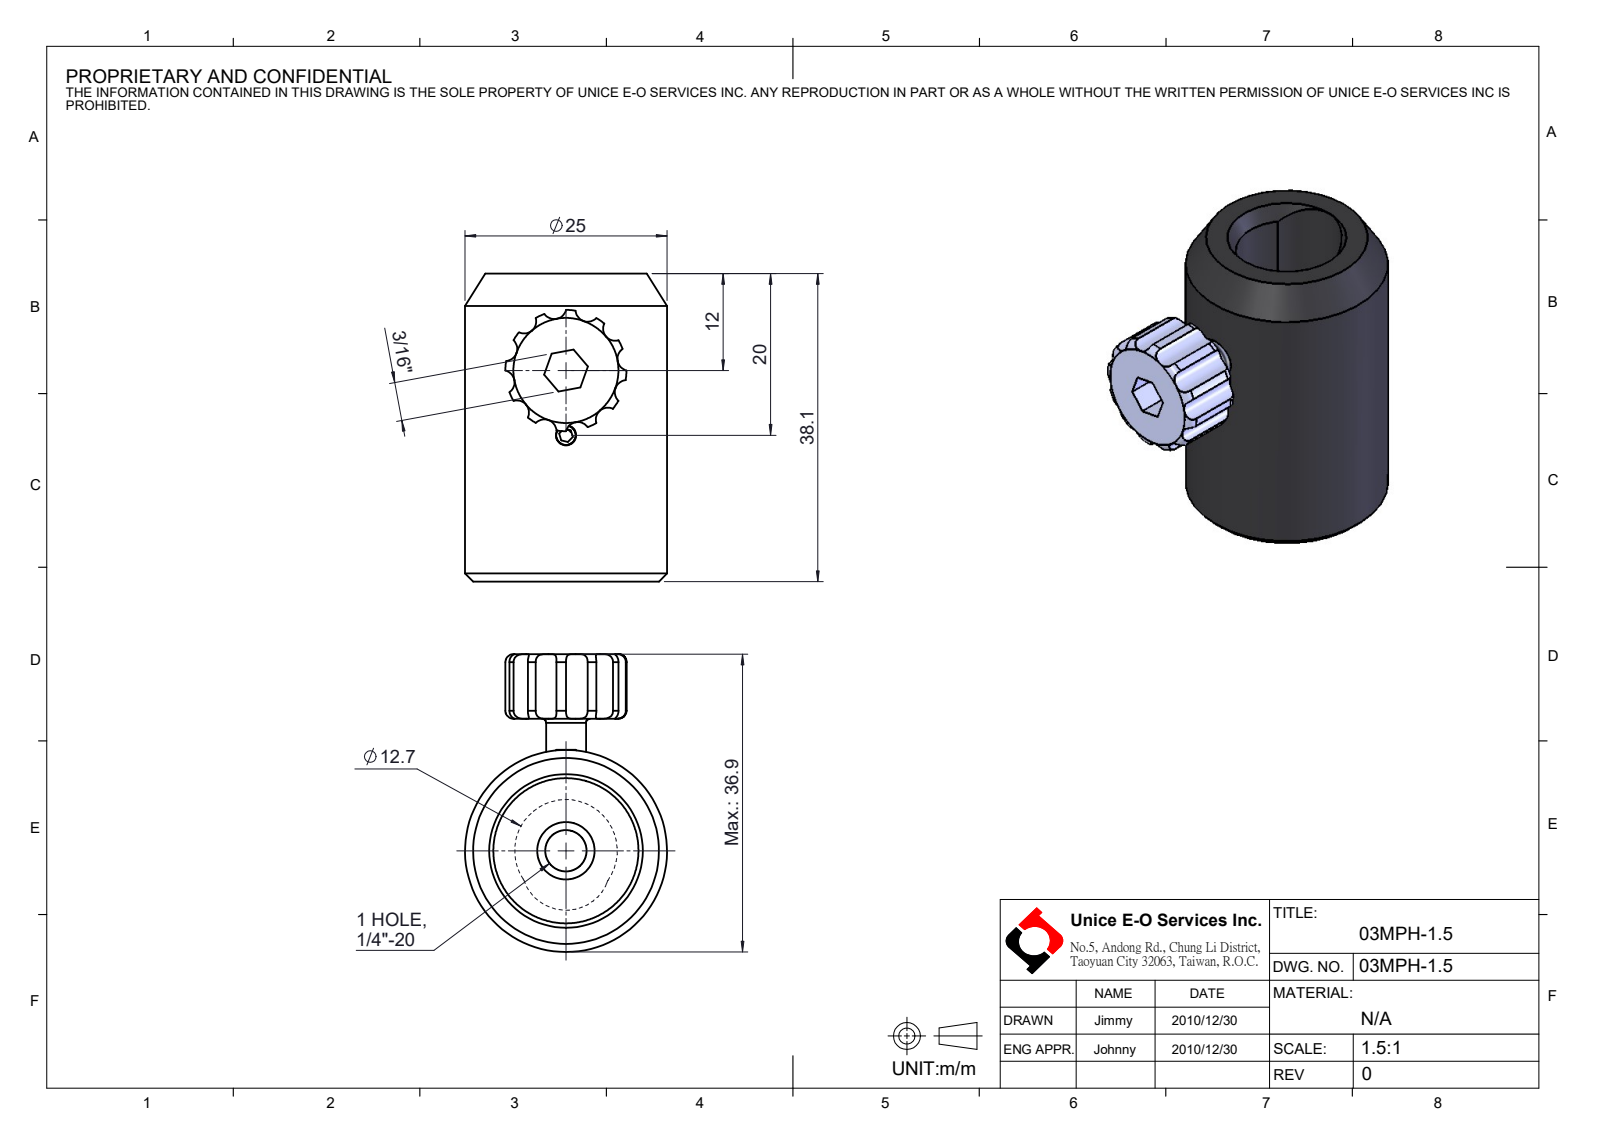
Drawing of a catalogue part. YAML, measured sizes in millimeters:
part_name: "03MPH-1.5"
step_written_by: "SolidWorks 2016 (CONFIG_CONTROL_DESIGN)"
units: millimeters
bodies: {solids: 0, faces: 96, planar: 16, cylindrical: 42, other: 38}
overall_size: [38.1, 36.85, 25]
round_holes:
  - {diameter: 2.5, count: 1}
  - {diameter: 5.11, count: 1}
  - {diameter: 19, count: 1}
round_bosses_or_shafts:
  - {diameter: 25, count: 1}
  - {diameter: 4.94, count: 1}
partial_cylinders:
  - {radius: 1.5, count: 12}
  - {radius: 5.5, count: 1}
  - {radius: 6.35, count: 1}
  - {radius: 7.5, count: 1}
face_to_face_distances: [38.1, 8, 4.76, 3.85, 11.85, 1.5]
